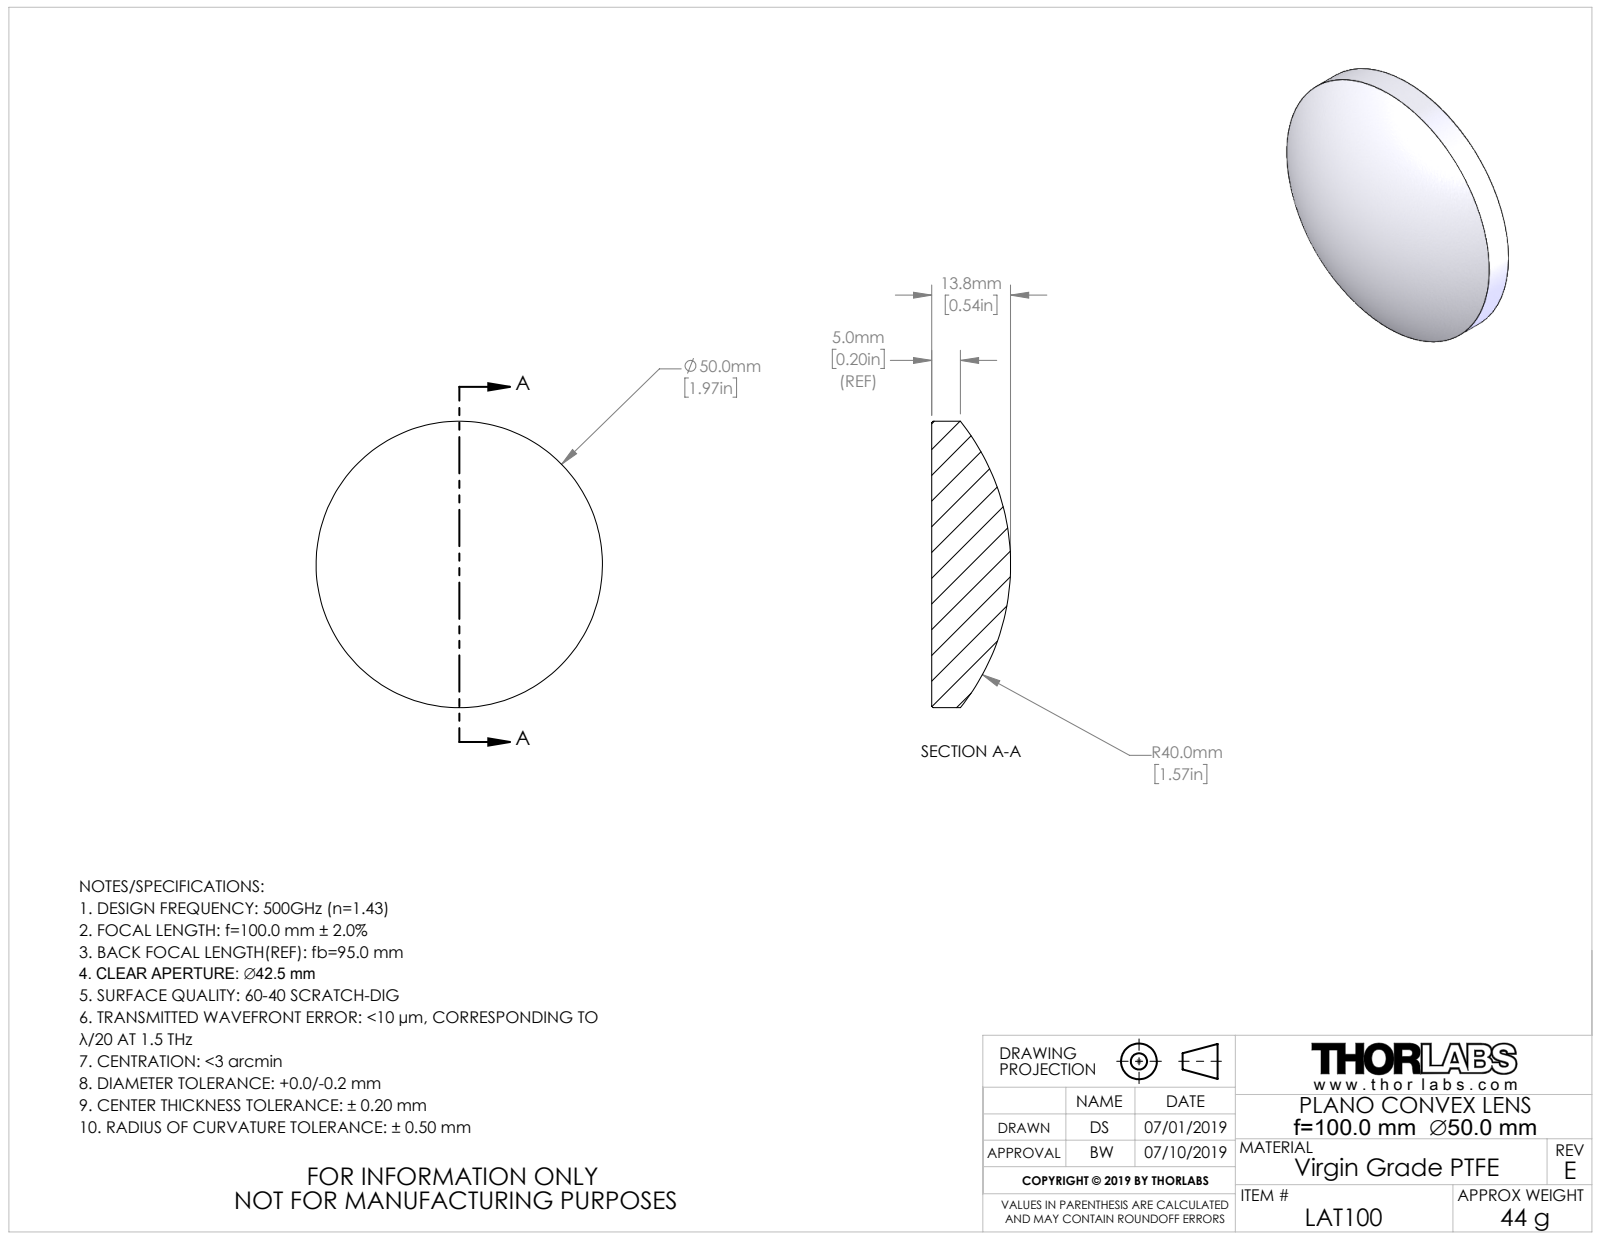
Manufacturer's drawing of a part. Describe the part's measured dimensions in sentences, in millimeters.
The part is named "12647-E0W". Its 3-D file was written by "SolidWorks 2018 (CONFIG_CONTROL_DESIGN)". It is 1 solid with 7 faces: 1 planar, 2 cylindrical and 4 other. Overall it measures 50 by 50 by 13.78 millimeters. Its volume is 18 791 cubic millimeters and its surface area 4 932 square millimeters. Round bosses or shafts: 1 of diameter 50.
